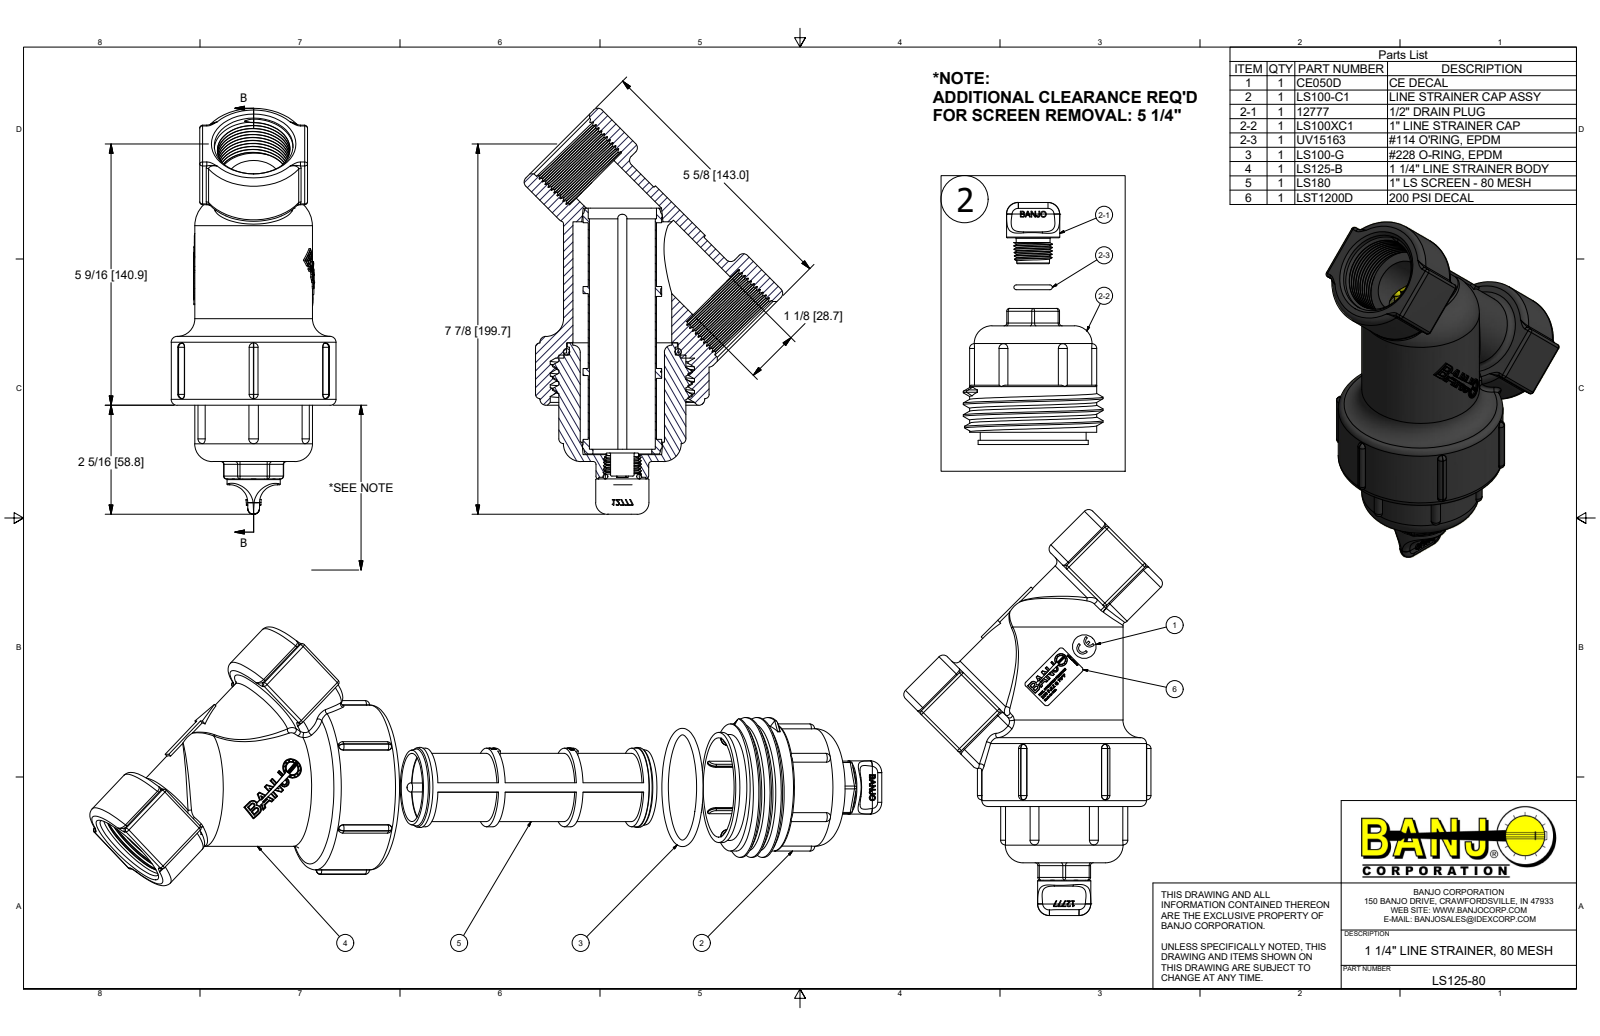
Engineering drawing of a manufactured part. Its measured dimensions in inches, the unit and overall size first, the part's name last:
Units: inches
Overall size (bounding box): 34.216 × 34.216 × 3.5
Round holes (diameter × count): ⌀1.13 ×2, ⌀0.181 ×1, ⌀0.257 ×1, ⌀0.272 ×1, ⌀0.385 ×1, ⌀0.5 ×1, ⌀1.005 ×1, ⌀1.25 ×1, ⌀1.4 ×1, ⌀2.1 ×1, ⌀2.11 ×1, ⌀2.371 ×1
Round bosses / shafts (diameter × count): ⌀3.5 ×1, ⌀2.971 ×1, ⌀2.7 ×1, ⌀2.5 ×1, ⌀2.34 ×1, ⌀2.25 ×1, ⌀1.67 ×1, ⌀1.45 ×1
Partial cylindrical surfaces — rounded edges, fillets, slot ends (radius × count): R0.06 ×54, R0.09 ×39, R0.03 ×19, R0.1 ×9, R0.15 ×6, R0.026 ×2, R0.033 ×2, R0.039 ×2
Main face-to-face distances: 0.2, 2.29, 2.05, 0.325, 1.26, 0.065, 1.06, 4.569, 2.375, 2.115
Hole centre spacings: 0.919
Volume: 24.13 in³ · Surface area: 1 353 in²
Bodies: 8 solids, 2311 faces (1191 planar, 333 cylindrical, 787 other)
Part name (STEP PRODUCT): LS125-80; LS125-B; LS100-C1; LS100XC1 (+6 more)
STEP written by: Autodesk Inventor 2018 (AUTOMOTIVE_DESIGN)
